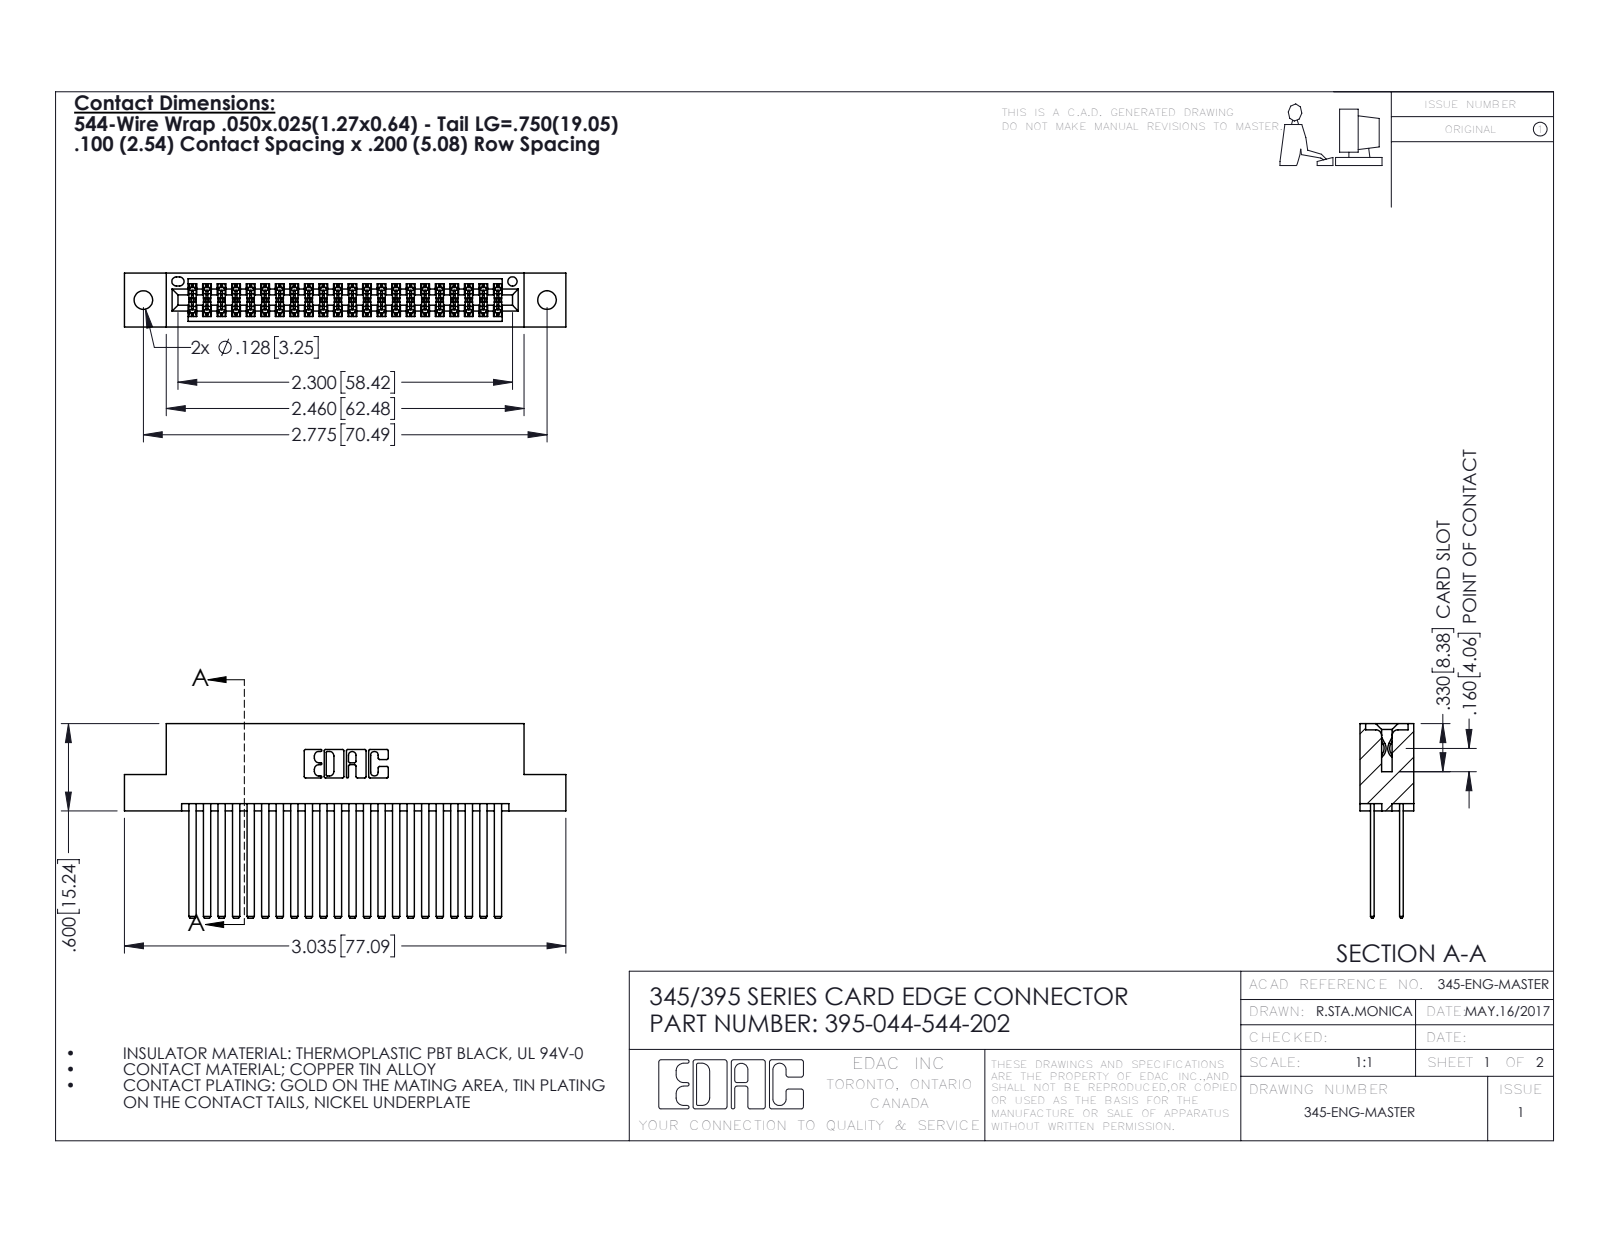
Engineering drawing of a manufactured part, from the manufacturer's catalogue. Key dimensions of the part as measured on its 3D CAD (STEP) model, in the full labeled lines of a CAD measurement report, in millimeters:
Part name (STEP PRODUCT): 395-044-544-202; 345-292-001_345-293-144; 345 Part_Flush Mounting Lugs - 0.128 Dia
STEP written by: SolidWorks 2016 (CONFIG_CONTROL_DESIGN)
Units: millimetres
Bodies: 45 solids, 2062 faces (1356 planar, 706 cylindrical, 0 other)
Overall size (bounding box): 77.1 × 34 × 9.4
Volume: 7 880 mm³ · Surface area: 12 800 mm²
Round holes (diameter × count): ⌀3.3 ×2, ⌀1.6 ×1
Partial cylindrical surfaces — rounded edges, fillets, slot ends (radius × count): R0.2 ×66, R0.3 ×22, R0.2 ×6, R0.8 ×6, R0.7 ×3, R0.4 ×2, R0.5 ×2, R0.6 ×2
Main face-to-face distances: 5.1, 7.6, 1.8, 2.5, 6.9, 0.6, 5.7, 9.4, 4.4, 1.3
Hole centre spacings: 6.9, 64.5, 70.5
